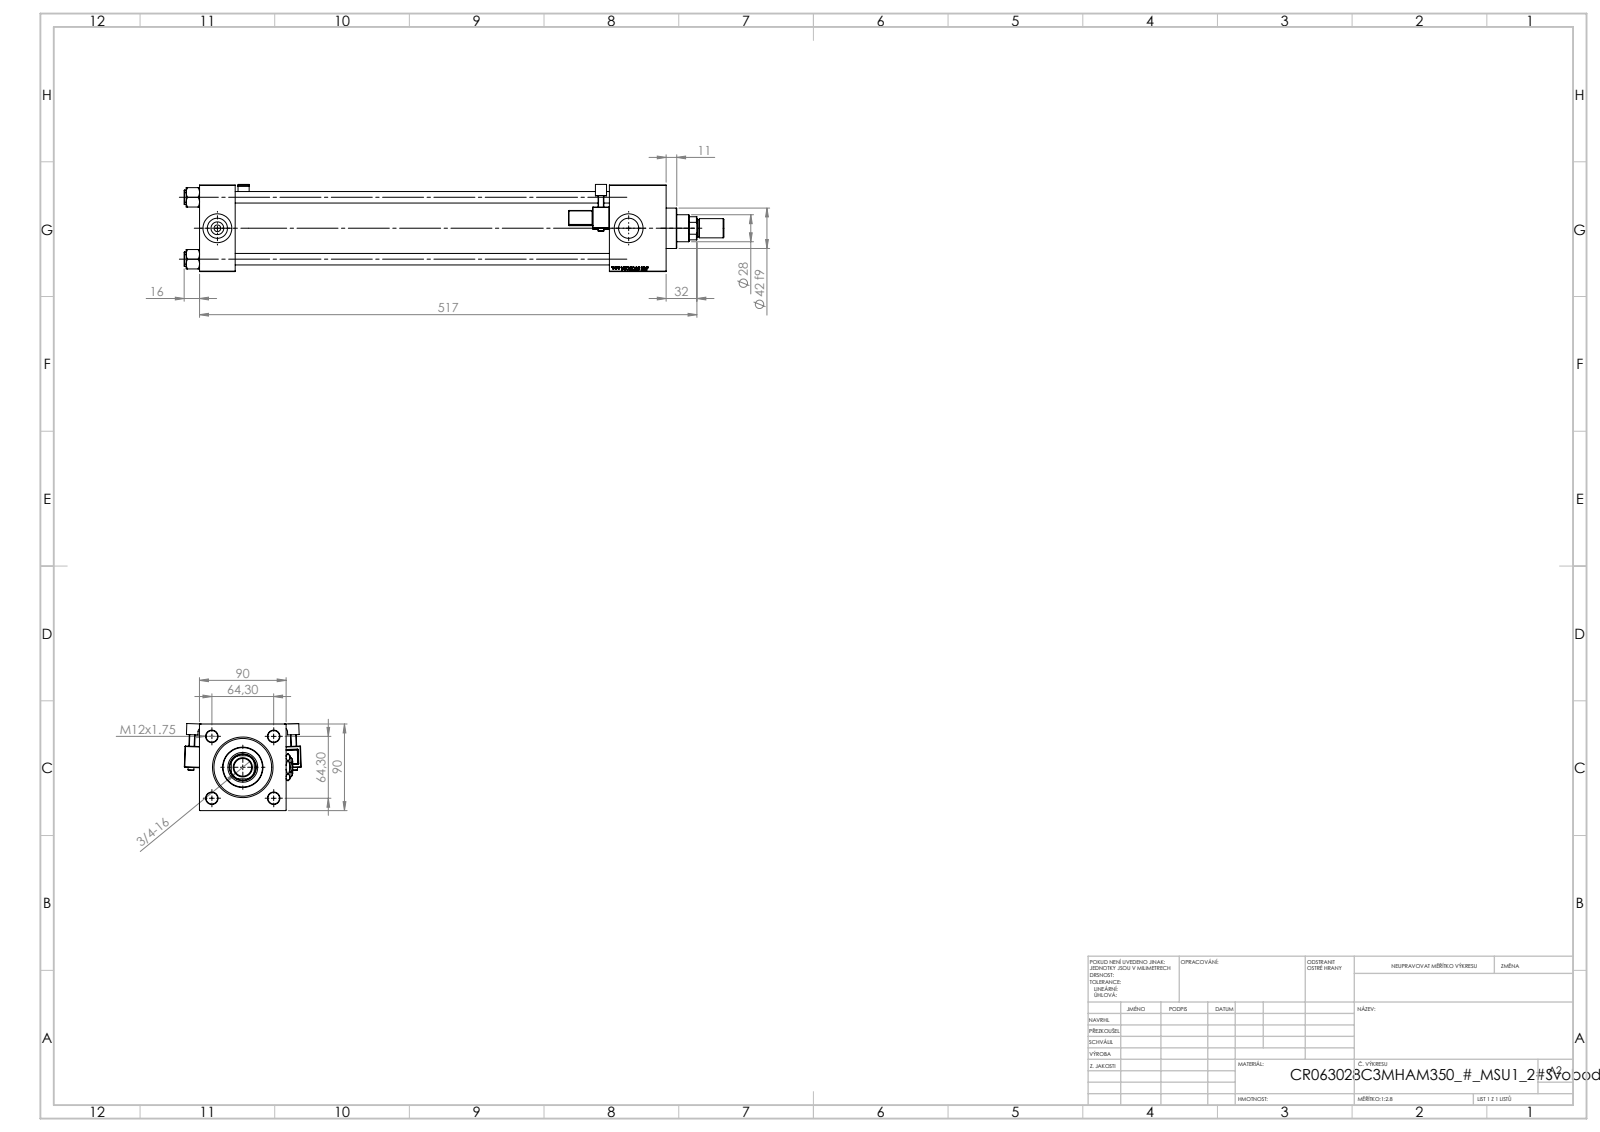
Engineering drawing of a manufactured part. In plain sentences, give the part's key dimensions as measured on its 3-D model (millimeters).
The part is named "V215_VC_A; V215CR_VCP_C; V215CR_C_Body; V215CR_MSU (+4 more)". Its 3-D file was written by "SolidWorks 2019 (CONFIG_CONTROL_DESIGN)". It is 16 solids with 1418 faces: 636 planar, 162 cylindrical and 620 other. Overall it measures 561 by 121.57 by 90.53 millimeters. Its volume is 1 548 000 cubic millimeters and its surface area 414 257 square millimeters. Round holes: 4 of diameter 12, 2 of diameter 7, 2 of diameter 20.96, 2 of diameter 30, 1 of diameter 18.5, 1 of diameter 28, 1 of diameter 31, 1 of diameter 50, 1 of diameter 60, 1 of diameter 63. Round bosses or shafts: 4 of diameter 15, 2 of diameter 6, 1 of diameter 69, 1 of diameter 42, 1 of diameter 20, 1 of diameter 18. Partial cylindrical surfaces (rounded edges, fillets, slot ends): 48 of radius 0.5, 2 of radius 1, 2 of radius 2.5, 2 of radius 4, 1 of radius 13.5. The main face-to-face distances are 90, 37, 485, 448, 426, 389, 59, 456.3, 419.3, 30.3. The hole center spacings are 45.47, 64.3, 90.93, 427.5.
